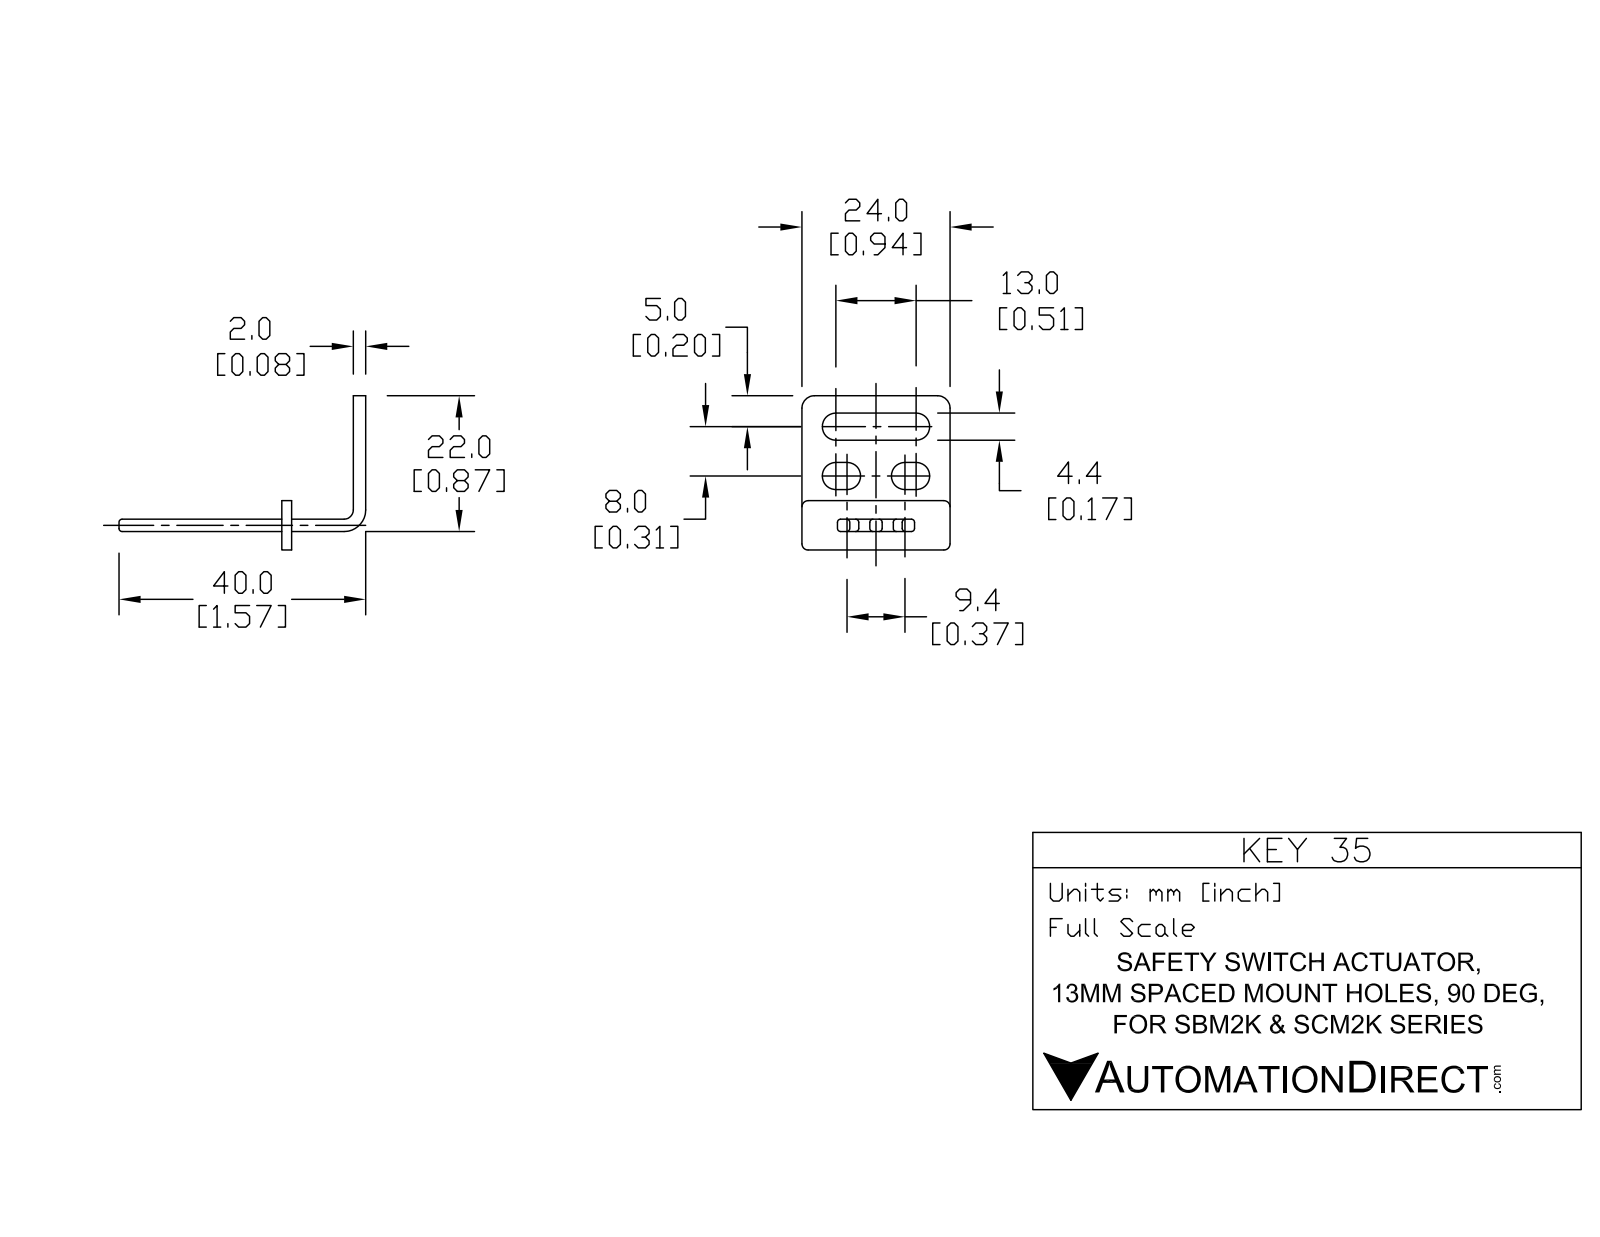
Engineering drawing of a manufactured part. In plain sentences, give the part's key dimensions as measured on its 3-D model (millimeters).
The part is named "KEY35". Its 3-D file was written by "SolidWorks 2019 (CONFIG_CONTROL_DESIGN)". It is 2 solids with 169 faces: 60 planar, 81 cylindrical and 28 other. Overall it measures 40 by 25 by 24 millimeters. Its volume is 1 970 cubic millimeters and its surface area 2 774 square millimeters. Partial cylindrical surfaces (rounded edges, fillets, slot ends): 42 of radius 0.5, 8 of radius 1, 6 of radius 2.2, 4 of radius 0.2, 4 of radius 1.5, 1 of radius 0.8, 1 of radius 2.8. The main face-to-face distances are 2, 12, 10, 13.6, 11.6, 1.6, 3, 5, 24, 5.7.
